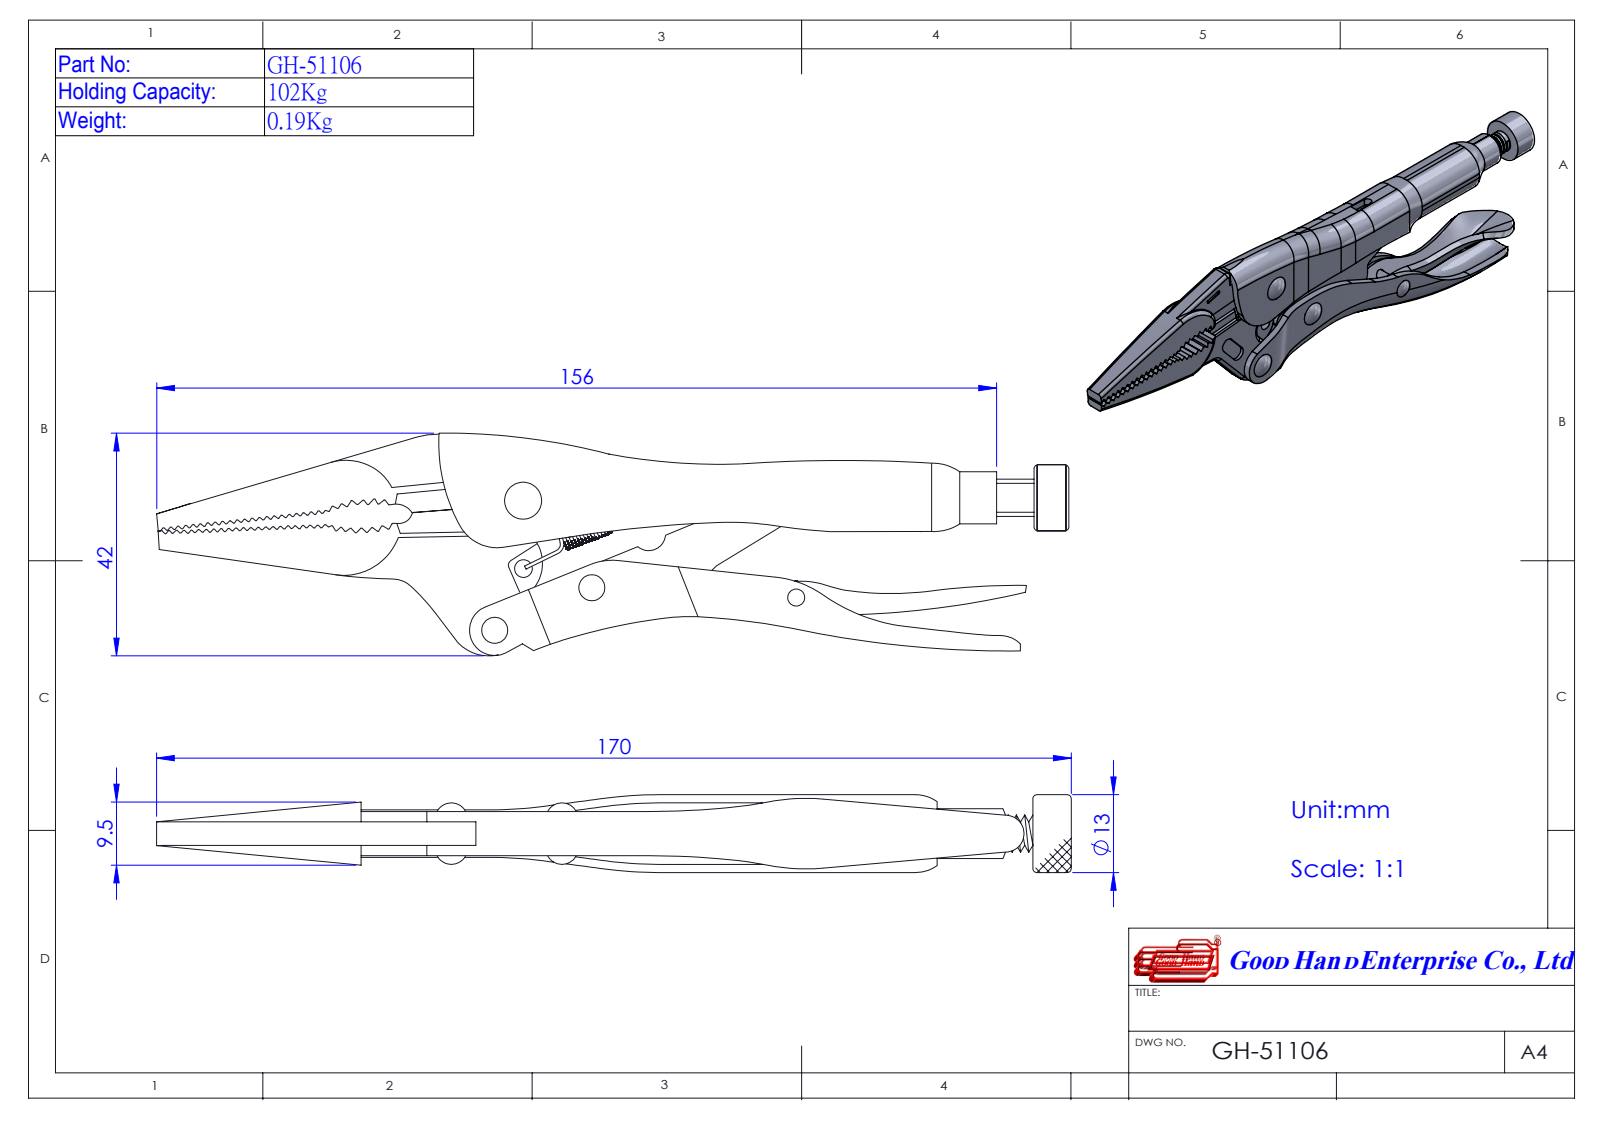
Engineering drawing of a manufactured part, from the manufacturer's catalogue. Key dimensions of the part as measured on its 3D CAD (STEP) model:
Part name (STEP PRODUCT): GH-51106(簡化); Group1^GH-51106(簡化)
STEP written by: SolidWorks 2016 (AUTOMOTIVE_DESIGN)
Units: millimetres
Bodies: 12 solids, 631 faces (224 planar, 253 cylindrical, 154 other)
Overall size (bounding box): 167.4 × 47.63 × 15.73
Volume: 25 859 mm³ · Surface area: 24 485 mm²
Round holes (diameter × count): ⌀5.2 ×1
Round bosses / shafts (diameter × count): ⌀4.8 ×3, ⌀0.75 ×2, ⌀12 ×1, ⌀9.2 ×1, ⌀6.1 ×1, ⌀5.3 ×1, ⌀4.3 ×1, ⌀2.95 ×1
Partial cylindrical surfaces — rounded edges, fillets, slot ends (radius × count): R1 ×17, R3 ×10, R0.5 ×7, R2 ×7, R5 ×5, R6 ×5, R4 ×4, R50 ×4
Main face-to-face distances: 2, 7.35, 4.3, 0.8, 3.05, 1.85, 9.45, 2.1, 2.25, 6.55
